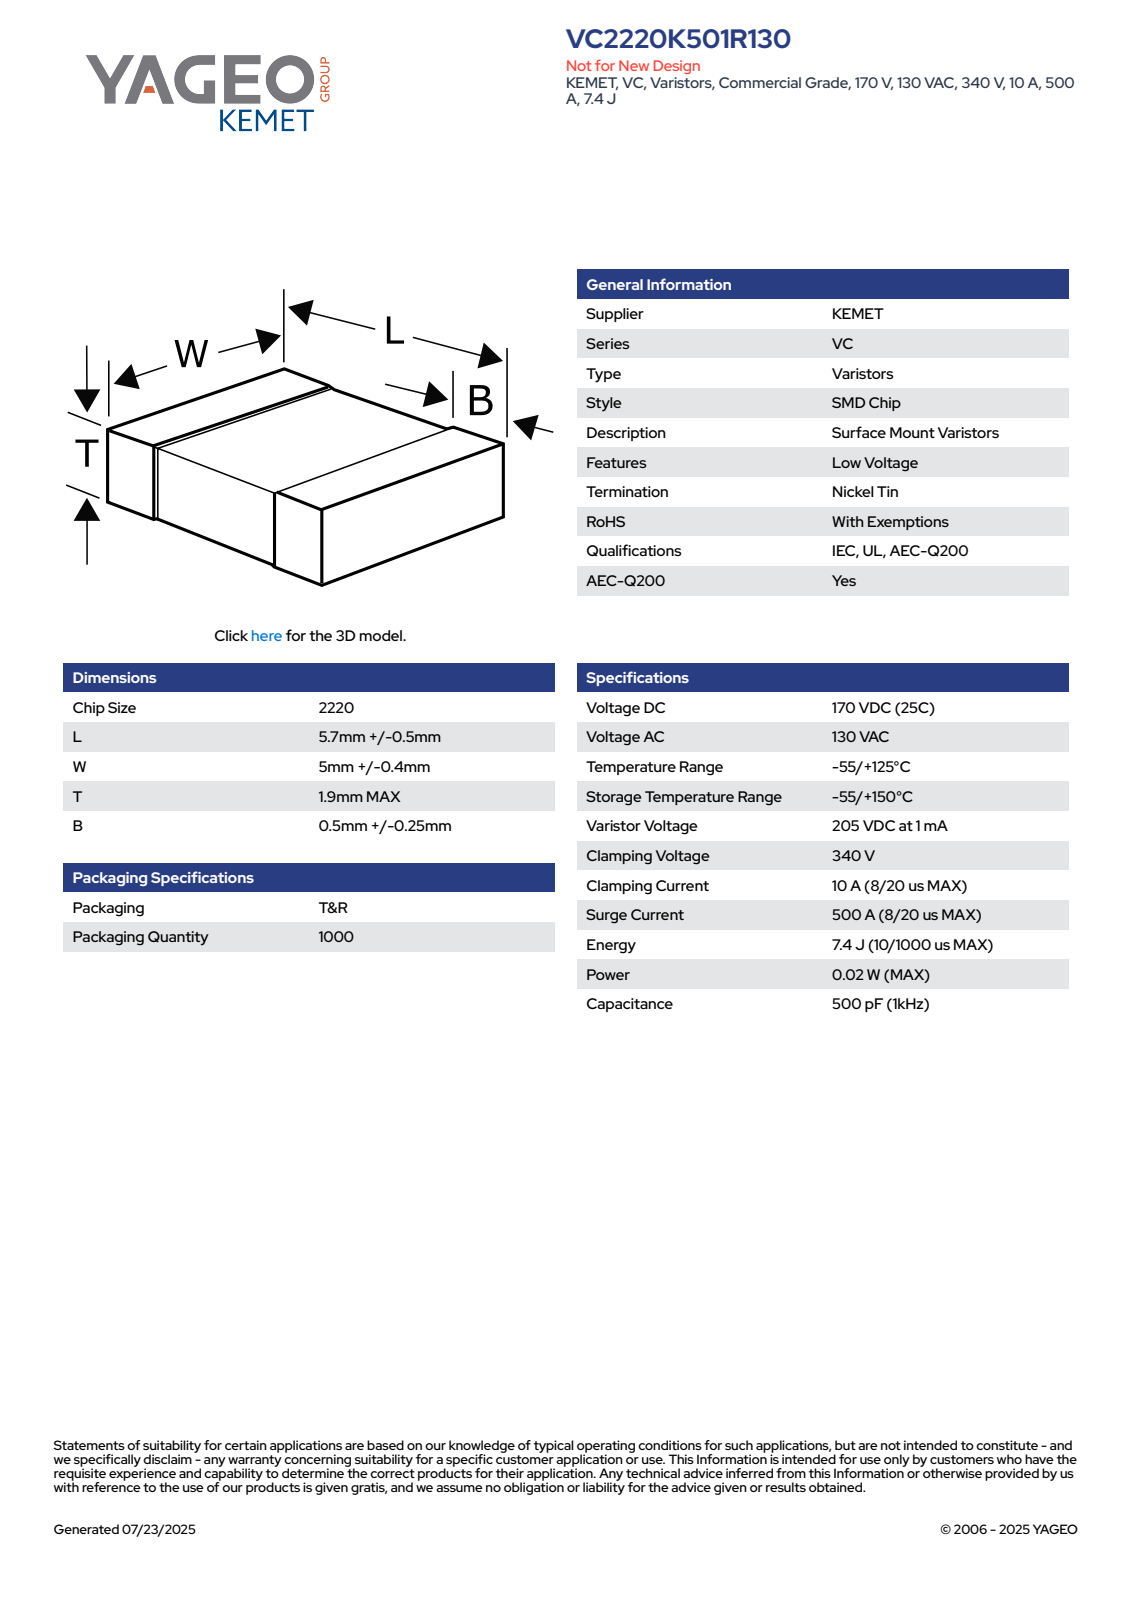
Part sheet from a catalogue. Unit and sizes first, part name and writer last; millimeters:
Units: millimetres
Overall size (bounding box): 6.2 × 5.4 × 1.9
Partial cylindrical surfaces — rounded edges, fillets, slot ends (radius × count): R0.11 ×24
Main face-to-face distances: 1.68, 1.79, 6.2, 5.18, 1.9, 5.29, 5.4, 2.85, 3.35, 0.8
Volume: 56 mm³ · Surface area: 110 mm²
Bodies: 4 solids, 125 faces (71 planar, 38 cylindrical, 16 other)
Part name (STEP PRODUCT): VS_SMD_2220_L6.20W5.4T1.9B0.75
STEP written by: SolidWorks 2014 (AUTOMOTIVE_DESIGN)
